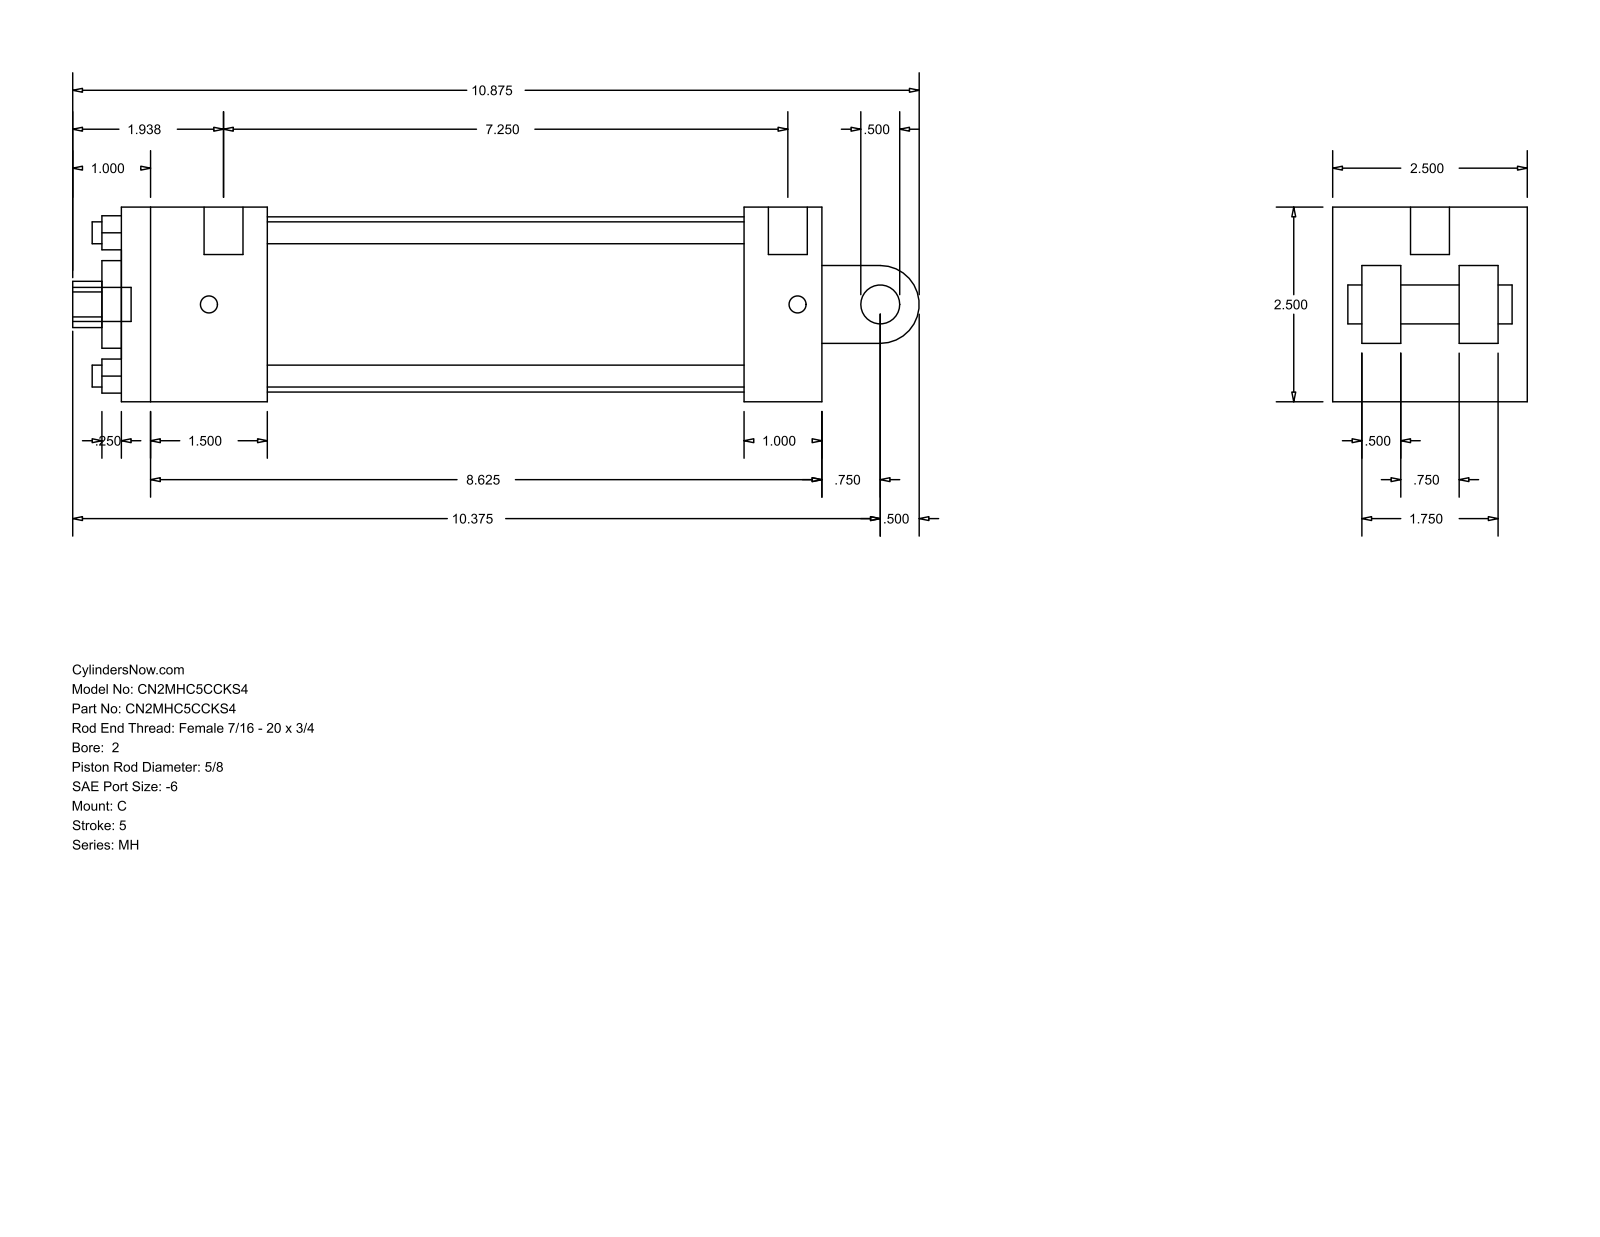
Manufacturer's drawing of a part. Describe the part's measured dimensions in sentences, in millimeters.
The part is named "MH_C__0200_0.625". Its 3-D file was written by "GSSL Pune (CONFIG_CONTROL_DESIGN)". It is 0 solids with 99 faces: 70 planar, 29 cylindrical and 0 other. Overall it measures 276.23 by 63.5 by 63.5 millimeters. Round holes: 4 of diameter 7.14, 2 of diameter 5.56, 1 of diameter 12.7, 1 of diameter 15.88, 1 of diameter 28.57, 1 of diameter 57.15. Round bosses or shafts: 2 of diameter 12.7, 2 of diameter 5.56, 1 of diameter 11.11. Partial cylindrical surfaces (rounded edges, fillets, slot ends): 1 of radius 7.54, 1 of radius 12.7. The main face-to-face distances are 63.5, 228.59, 25.4, 12.7, 9.52, 47.62, 203.19, 155.57, 180.97, 19.05. The hole center spacings are 33.05, 46.74, 66.1, 3.18.
